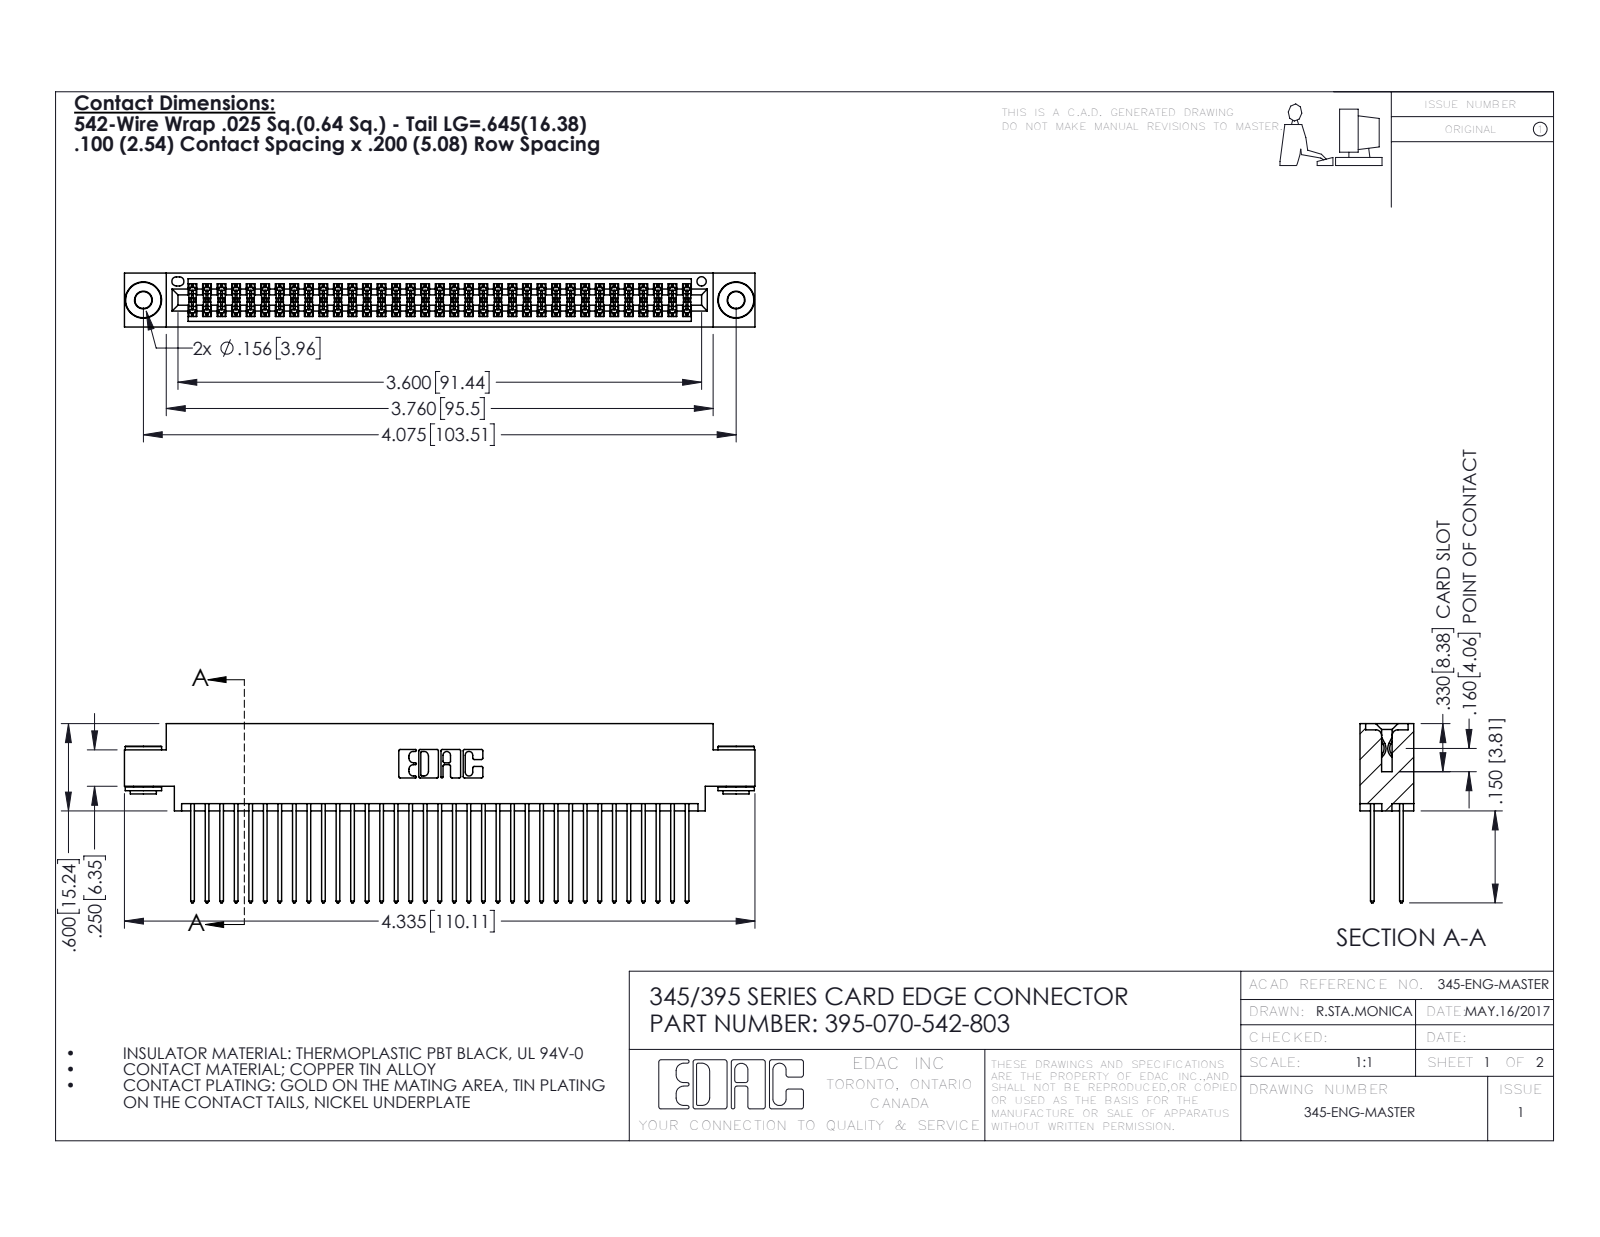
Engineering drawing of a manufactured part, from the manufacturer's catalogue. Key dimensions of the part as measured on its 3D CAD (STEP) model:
Part name (STEP PRODUCT): 345-292-001_345-293-142; 345-250-002_345-250-002-102; 395-070-542-803; 345 Part_0.170 Offset - 0.156 Dia-TH
STEP written by: SolidWorks 2016 (CONFIG_CONTROL_DESIGN)
Units: inches
Bodies: 73 solids, 3668 faces (2404 planar, 1256 cylindrical, 8 other)
Overall size (bounding box): 4.335 × 1.232 × 0.37
Volume: 0.663 in³ · Surface area: 27.58 in²
Round holes (diameter × count): ⌀0.116 ×2, ⌀0.156 ×2, ⌀0.064 ×1
Round bosses / shafts (diameter × count): ⌀0.25 ×2, ⌀0.18 ×2, ⌀0.136 ×2
Partial cylindrical surfaces — rounded edges, fillets, slot ends (radius × count): R0.006 ×105, R0.01 ×70, R0.01 ×22, R0.007 ×6, R0.031 ×6, R0.026 ×3, R0.014 ×2, R0.019 ×2
Main face-to-face distances: 0.072, 0.298, 0.2, 0.098, 0.272, 0.025, 0.37, 0.225, 0.175, 0.149
Hole centre spacings: 0.27, 3.839, 4.075
